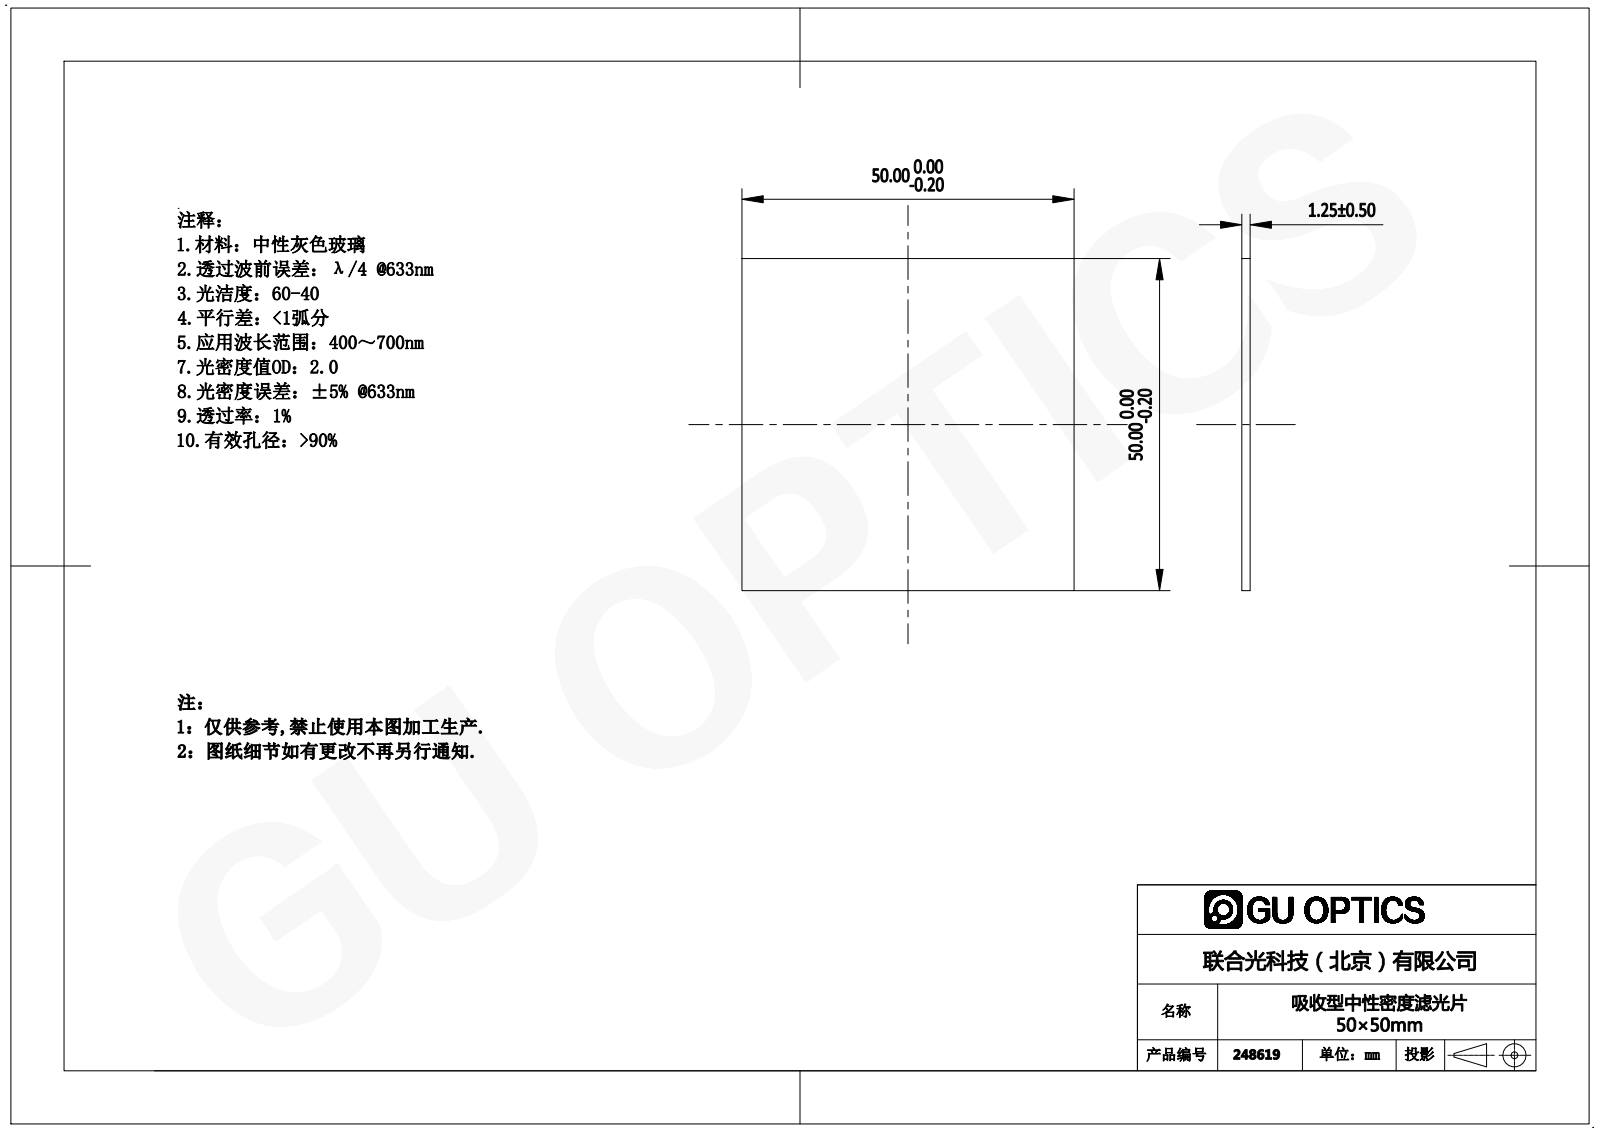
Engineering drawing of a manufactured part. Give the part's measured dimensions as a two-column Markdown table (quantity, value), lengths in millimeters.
| quantity | value |
| --- | --- |
| part name | 248619 |
| STEP written by | SolidWorks 2016 (AUTOMOTIVE_DESIGN) |
| units | millimeters |
| bodies | 1 solid, 6 faces (6 planar, 0 cylindrical, 0 other) |
| overall size | 50 × 50 × 1.25 |
| volume | 3 125 mm³ |
| surface area | 5 250 mm² |
| main face-to-face distances | 1.25, 50 |
